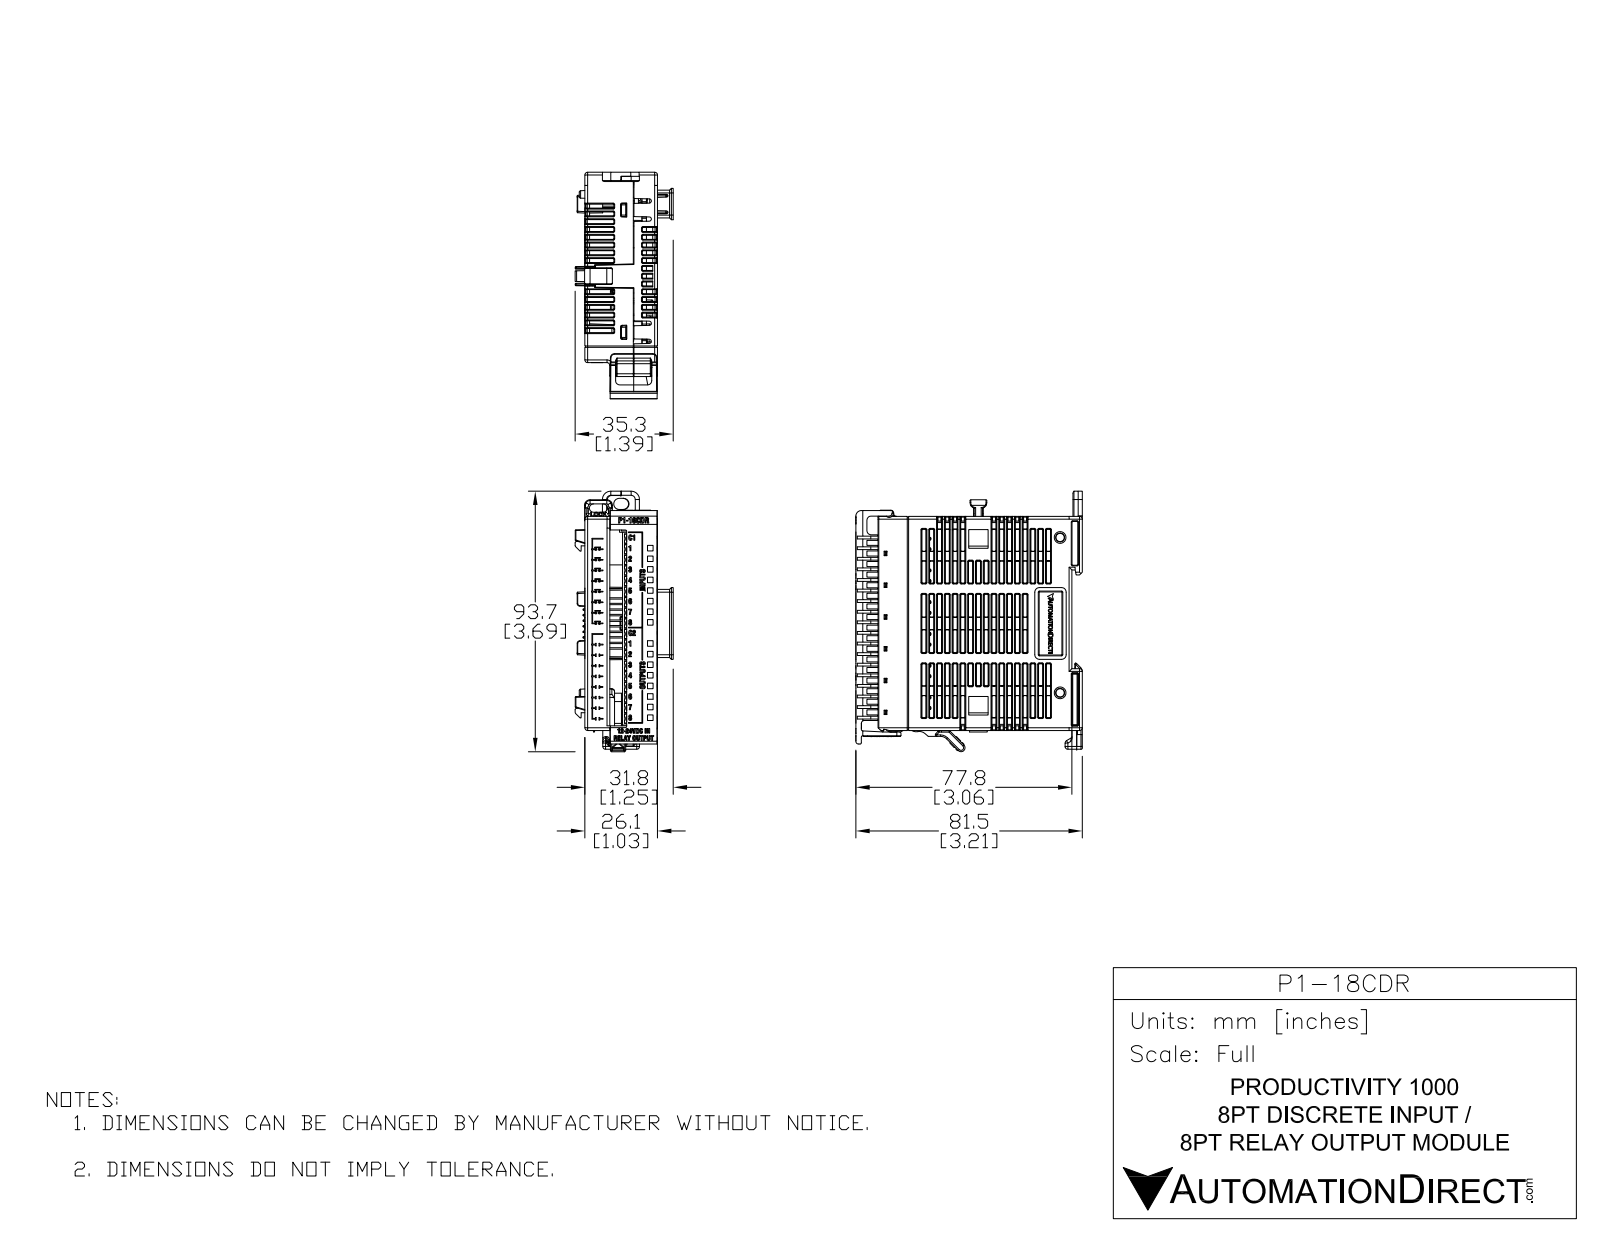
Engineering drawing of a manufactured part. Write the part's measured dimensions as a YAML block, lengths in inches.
part_name: "P1-16CDR Red 1 w latch ext comb coord B fXT r1b"
step_written_by: "SolidWorks 2017 (AUTOMOTIVE_DESIGN)"
units: inches
bodies: {solids: 9, faces: 5643, planar: 3882, cylindrical: 868, other: 893}
overall_size: [3.69, 3.219, 1.389]
volume: 8.211
surface_area: 67.48
round_holes:
  - {diameter: 0.01, count: 20}
  - {diameter: 0.016, count: 16}
  - {diameter: 0.016, count: 2}
  - {diameter: 0.024, count: 2}
  - {diameter: 0.049, count: 1}
round_bosses_or_shafts:
  - {diameter: 0.064, count: 1}
partial_cylinders:
  - {radius: 0.02, count: 139}
  - {radius: 0.01, count: 104}
  - {radius: 0.012, count: 85}
  - {radius: 0.008, count: 82}
  - {radius: 0.039, count: 70}
  - {radius: 0.062, count: 18}
  - {radius: 0.079, count: 12}
  - {radius: 0.059, count: 11}
face_to_face_distances: [1.03, 2.318, 3.031, 2.983, 0.665, 0.067, 0.15, 0.079, 0.6, 0.148]
hole_center_spacings: [0.079, 0.6, 0.15, 0.75, 0.45, 0.157, 0.3, 1.199]
